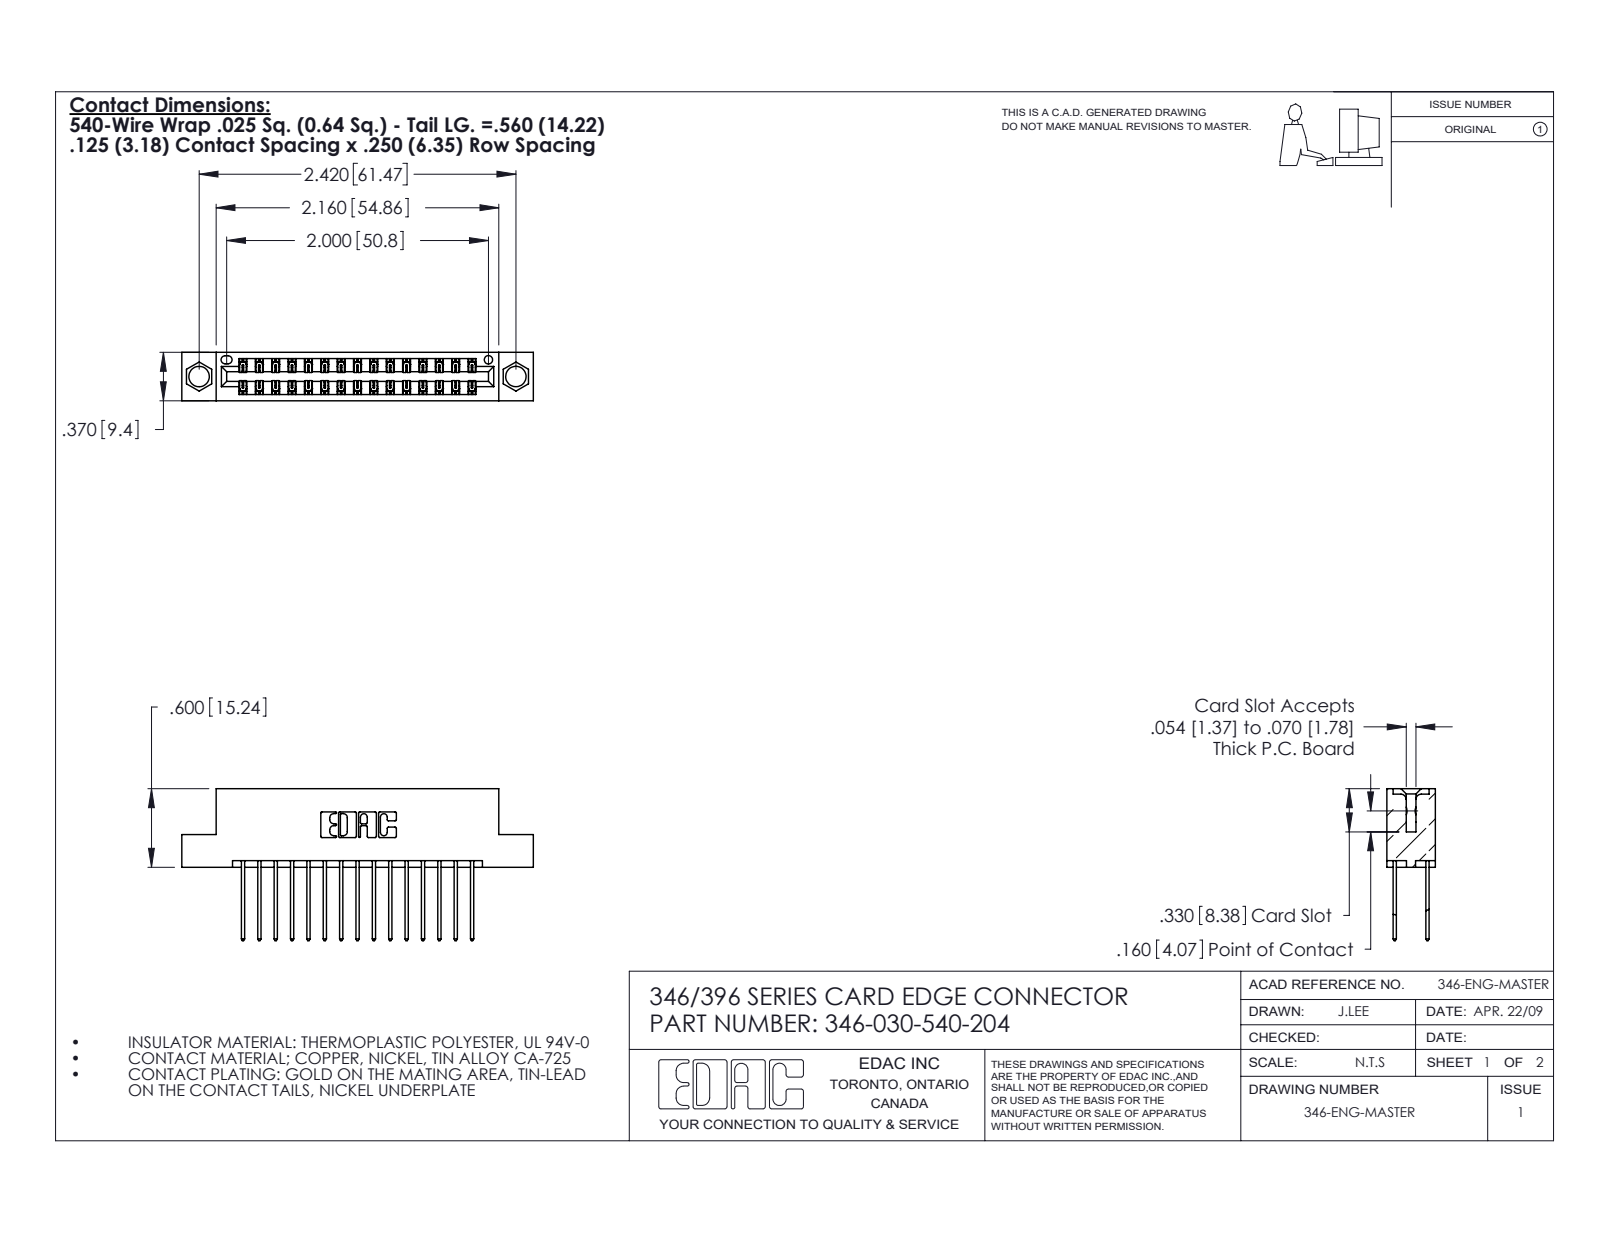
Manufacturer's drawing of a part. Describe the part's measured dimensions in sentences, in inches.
The part is named "345-292-001_345-293-140; 346-030-540-204; 346 Part_Flush Mounting Lugs - 0.156 Dia-TH". Its 3-D file was written by "SolidWorks 2020 (CONFIG_CONTROL_DESIGN)". It is 31 solids with 1696 faces: 1140 planar, 556 cylindrical and 0 other. Overall it measures 2.685 by 1.16 by 0.37 inches. Its volume is 0.394 cubic inches and its surface area 13.68 square inches. Round holes: 2 of diameter 0.156, 1 of diameter 0.064. Partial cylindrical surfaces (rounded edges, fillets, slot ends): 45 of radius 0.006, 30 of radius 0.01, 22 of radius 0.01, 6 of radius 0.007, 6 of radius 0.031, 3 of radius 0.026, 2 of radius 0.014, 2 of radius 0.022. The main face-to-face distances are 0.048, 0.322, 0.25, 0.37, 0.072, 0.298, 0.025, 0.275, 0.148, 0.222. The hole center spacings are 0.246, 2.213, 2.42.
